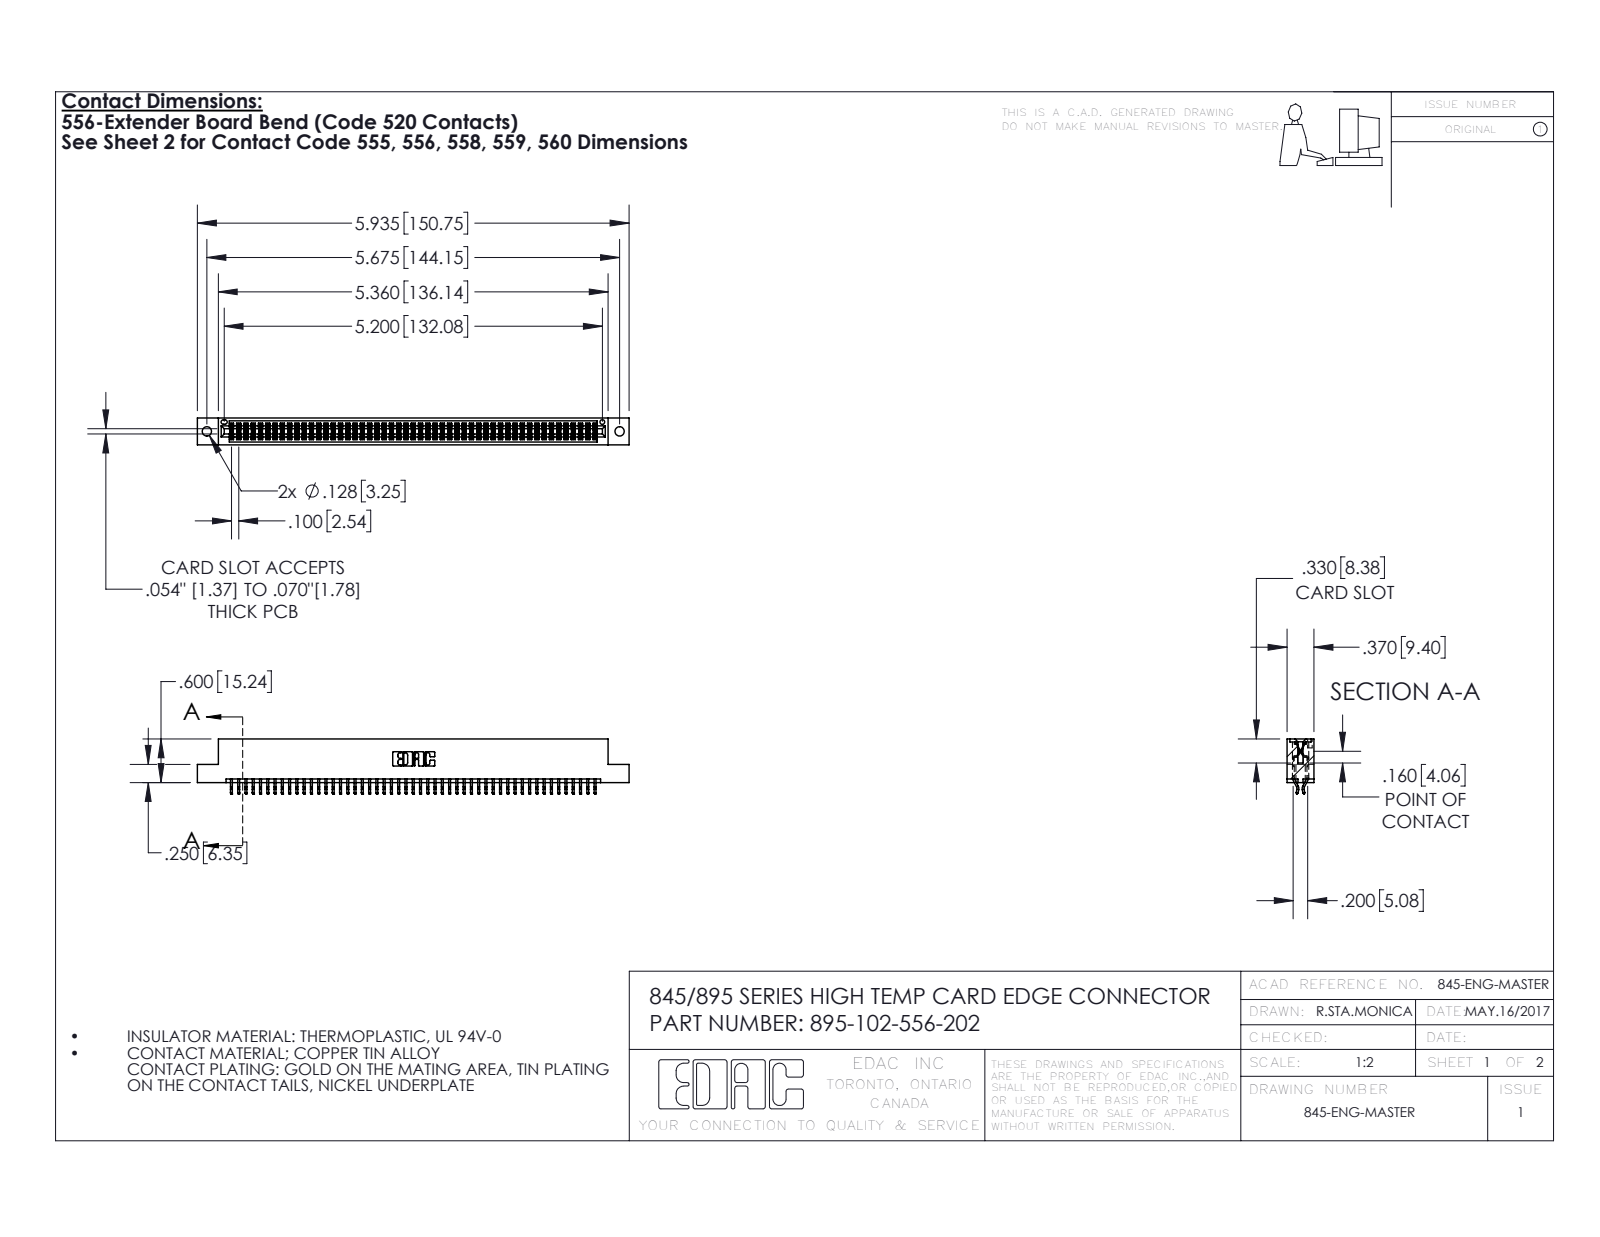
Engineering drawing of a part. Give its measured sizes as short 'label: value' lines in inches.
name: 395-102-556-202; 345-292-001_556 Tail; 345 Part_Flush Mounting Lugs - 0.128 Dia
written by: SolidWorks 2016 (CONFIG_CONTROL_DESIGN)
unit: in
bodies: 103 solids, 5838 faces (3854 planar, 1984 cylindrical, 0 other)
size: 5.935 × 0.757 × 0.37
volume: 0.896 in³; area: 33.36 in²
holes: 2× ⌀0.128, 1× ⌀0.064
rounds: 153× R0.006, 22× R0.01, 6× R0.007, 6× R0.031, 3× R0.026, 2× R0.01, 2× R0.014, 2× R0.019
face distances: 0.298, 0.072, 0.37, 0.2, 0.025, 0.098, 0.272, 0.225, 0.175, 0.149
hole spacings: 0.27, 5.439, 5.675
